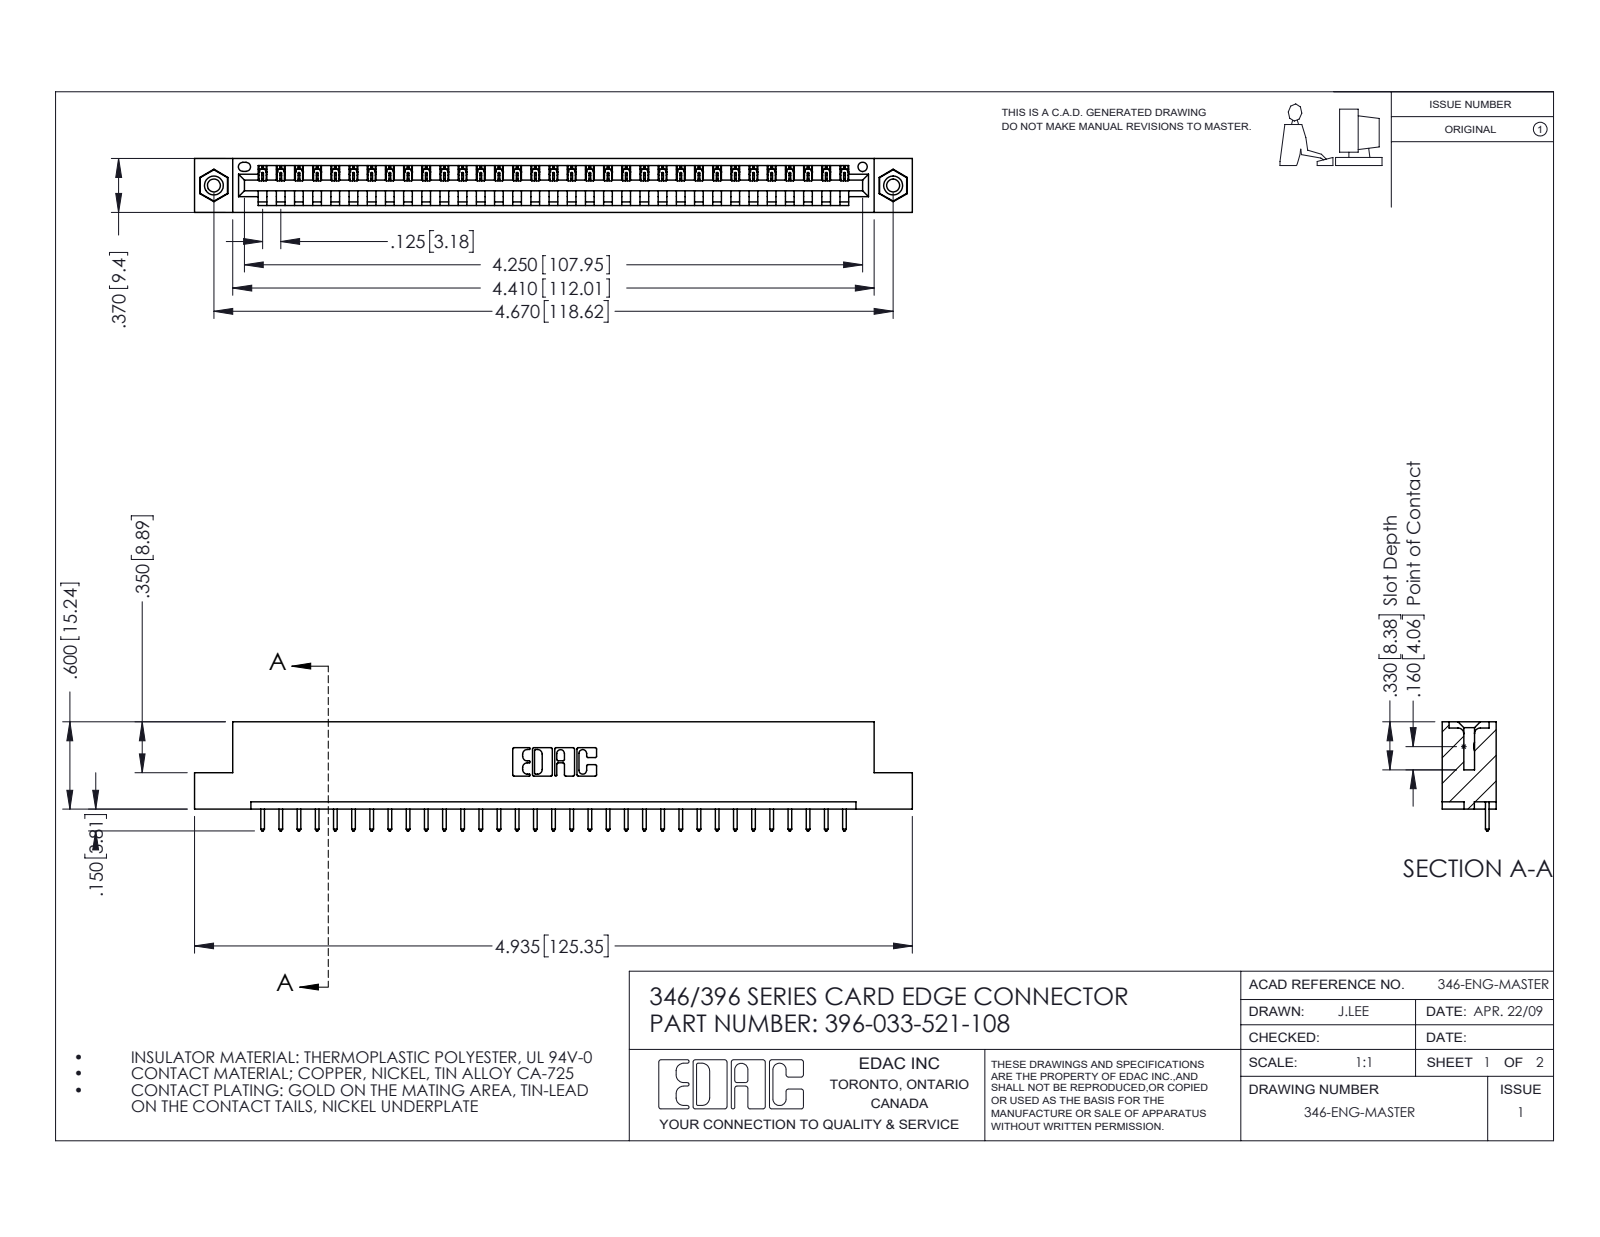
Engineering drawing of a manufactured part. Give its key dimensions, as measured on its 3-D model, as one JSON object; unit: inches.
{"part_name": "345-250-001_345-250-003-102; 396-033-521-108; 346 Part_Flush Mounting Lugs - 0.156 Dia-TI; 345-292-001_345-293-121", "step_written_by": "SolidWorks 2016 (CONFIG_CONTROL_DESIGN)", "units": "inches", "bodies": {"solids": 36, "faces": 2096, "planar": 1428, "cylindrical": 652, "other": 16}, "overall_size": [4.935, 0.75, 0.37], "volume_in3": 0.722, "surface_area_in2": 22.23, "round_holes": [[0.089, 2], [0.125, 2], [0.156, 2], [0.064, 1]], "round_bosses_or_shafts": [[0.155, 2]], "partial_cylinders_radius": [[0.006, 66], [0.01, 66], [0.01, 22], [0.007, 6], [0.031, 6], [0.026, 3], [0.031, 2], [0.04, 2]], "face_to_face_distances": [0.048, 0.322, 0.37, 0.25, 0.072, 0.298, 0.025, 0.148, 0.222, 0.1], "hole_center_spacings": [0.246, 4.462, 4.67]}
